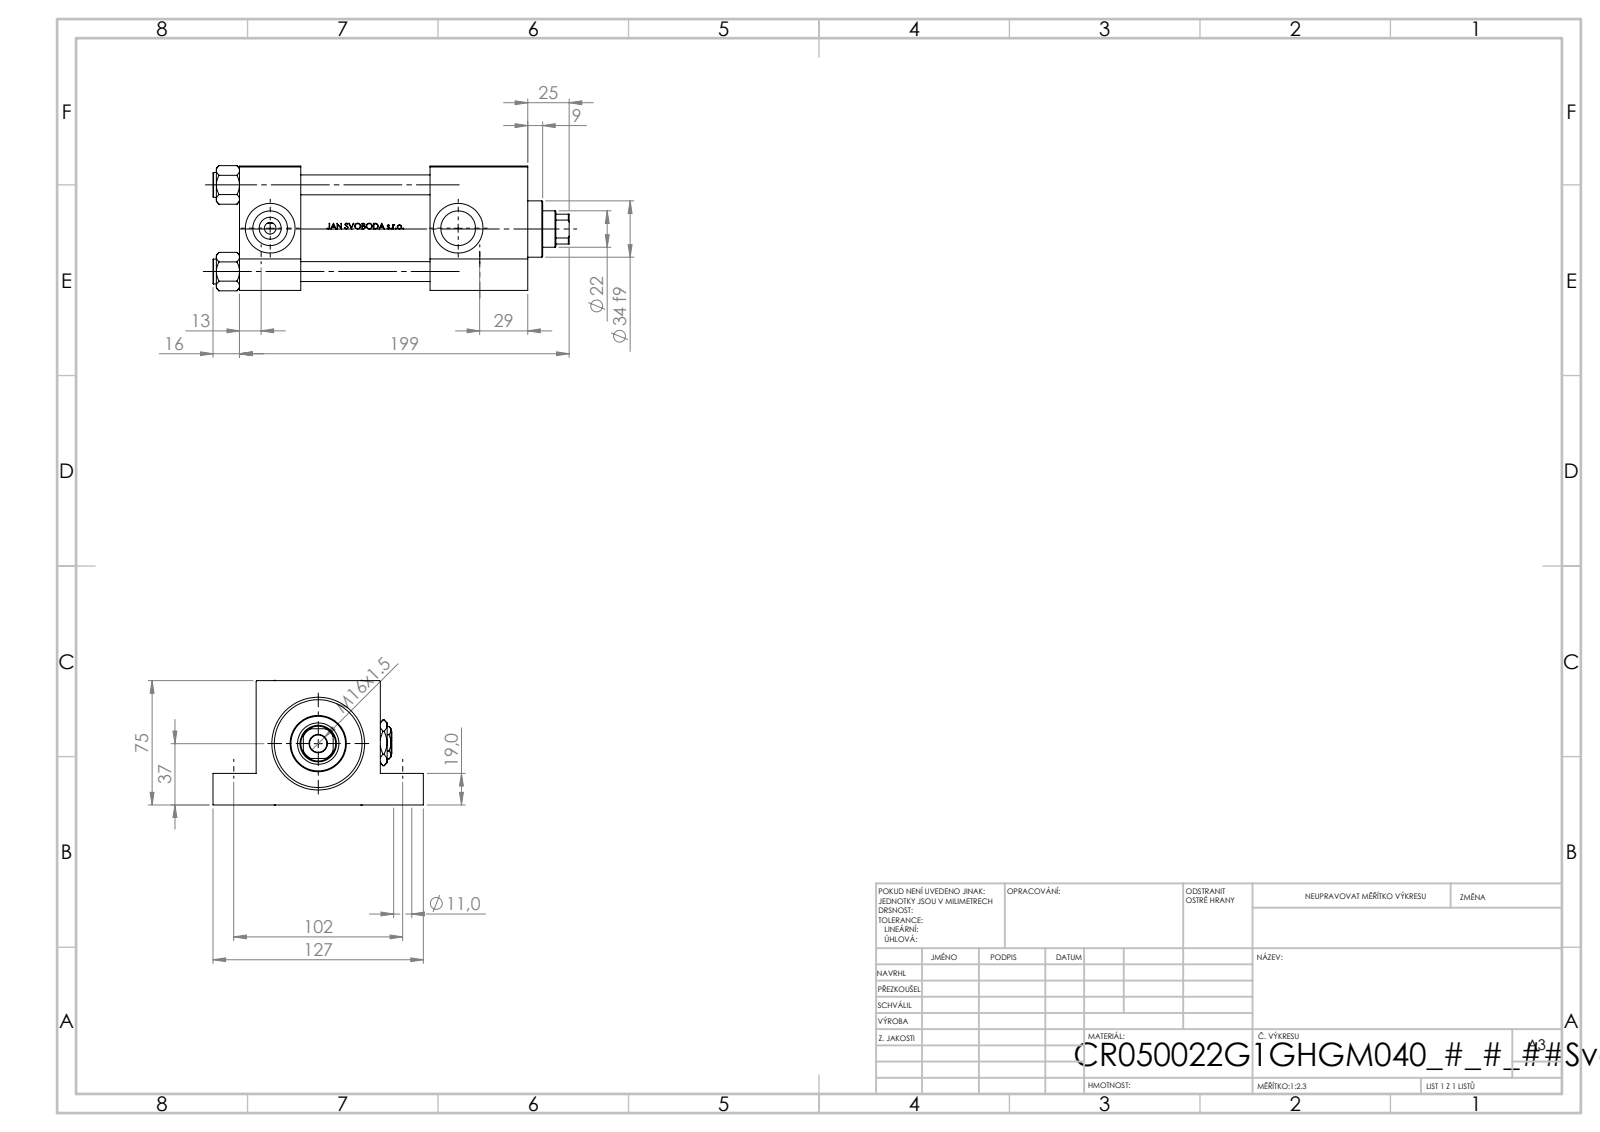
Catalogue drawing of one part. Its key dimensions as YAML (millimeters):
part_name: "V215CR_G_TYCINKA; NUT_M5_G; V215_VC_A; V215CR_VCP_G (+2 more)"
step_written_by: "SolidWorks 2019 (CONFIG_CONTROL_DESIGN)"
units: millimeters
bodies: {solids: 12, faces: 1134, planar: 454, cylindrical: 128, other: 552}
overall_size: [215, 127, 75.54]
volume: 779044
surface_area: 172362
round_holes:
  - {diameter: 11, count: 4}
  - {diameter: 12, count: 4}
  - {diameter: 7, count: 2}
  - {diameter: 20.96, count: 2}
  - {diameter: 30, count: 2}
  - {diameter: 10.5, count: 1}
  - {diameter: 22, count: 1}
  - {diameter: 25, count: 1}
  - {diameter: 41, count: 1}
  - {diameter: 50, count: 1}
  - {diameter: 53, count: 1}
round_bosses_or_shafts:
  - {diameter: 15, count: 4}
  - {diameter: 56, count: 1}
  - {diameter: 34, count: 1}
partial_cylinders:
  - {radius: 10.5, count: 1}
face_to_face_distances: [75, 37, 174, 137, 19, 56, 115, 78, 59, 26]
hole_center_spacings: [52.3, 36.63, 37.34, 73.96, 102, 132, 166.82, 113.5]
